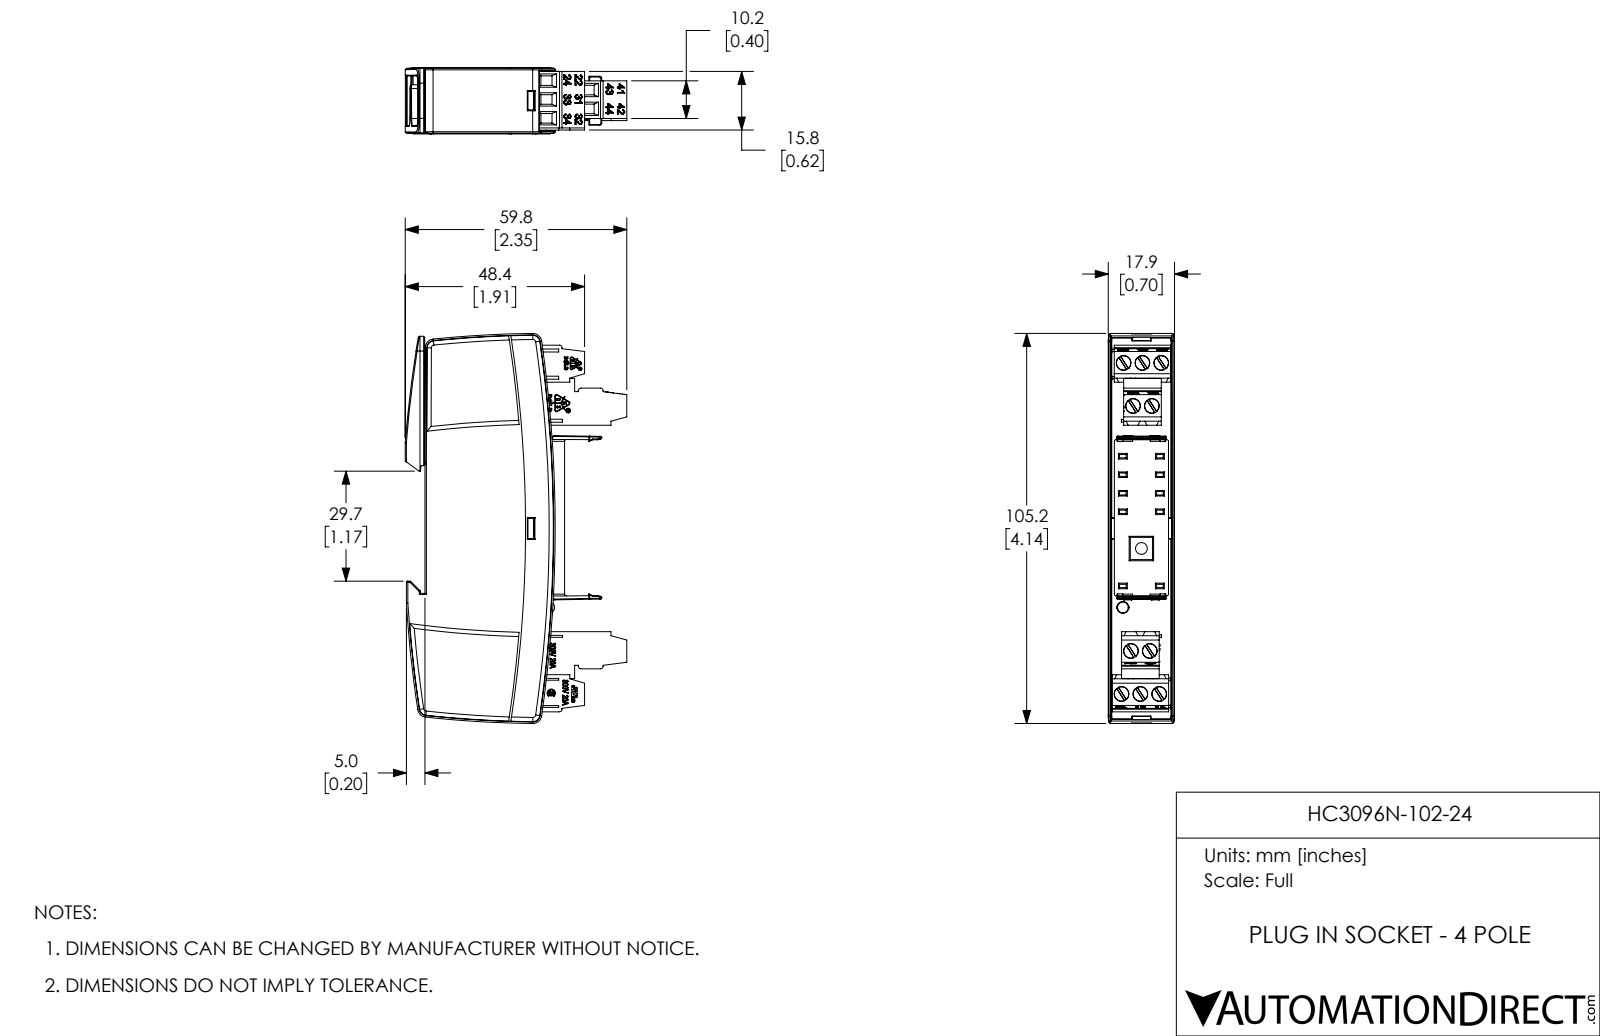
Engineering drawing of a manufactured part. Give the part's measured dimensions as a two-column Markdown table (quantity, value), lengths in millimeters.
| quantity | value |
| --- | --- |
| part name | HC3096N-102-24 |
| STEP written by | SolidWorks 2017 (AUTOMOTIVE_DESIGN) |
| units | millimeters |
| bodies | 1 solid, 3646 faces (2404 planar, 678 cylindrical, 564 other) |
| overall size | 105.2 × 59.8 × 17.9 |
| volume | 71 120 mm³ |
| surface area | 23 150 mm² |
| round holes (diameter × count) | 1.5 × 20, 4 × 10, 0.6 × 4, 0.9 × 2, 0.9 × 2, 1.3 × 2, 2.4 × 1, 3.2 × 1 |
| round bosses / shafts (diameter × count) | 3.9 × 10, 0.5 × 4, 1.2 × 2, 0.9 × 2, 3.2 × 1, 2.9 × 1 |
| partial cylindrical surfaces (radius × count) | 0.2 × 51, 0.3 × 14, 0.1 × 12, 0.2 × 12, 0.5 × 11, 0.1 × 8, 0.1 × 8, 0.2 × 8 |
| main face-to-face distances | 17.7, 17.9, 17.5, 1.7, 0.6, 16.1, 16.3, 1.4, 10.2, 29.3 |
| hole center spacings | 10, 5.1, 11.9, 15.4, 5, 11.2, 3.6, 6.2 |
